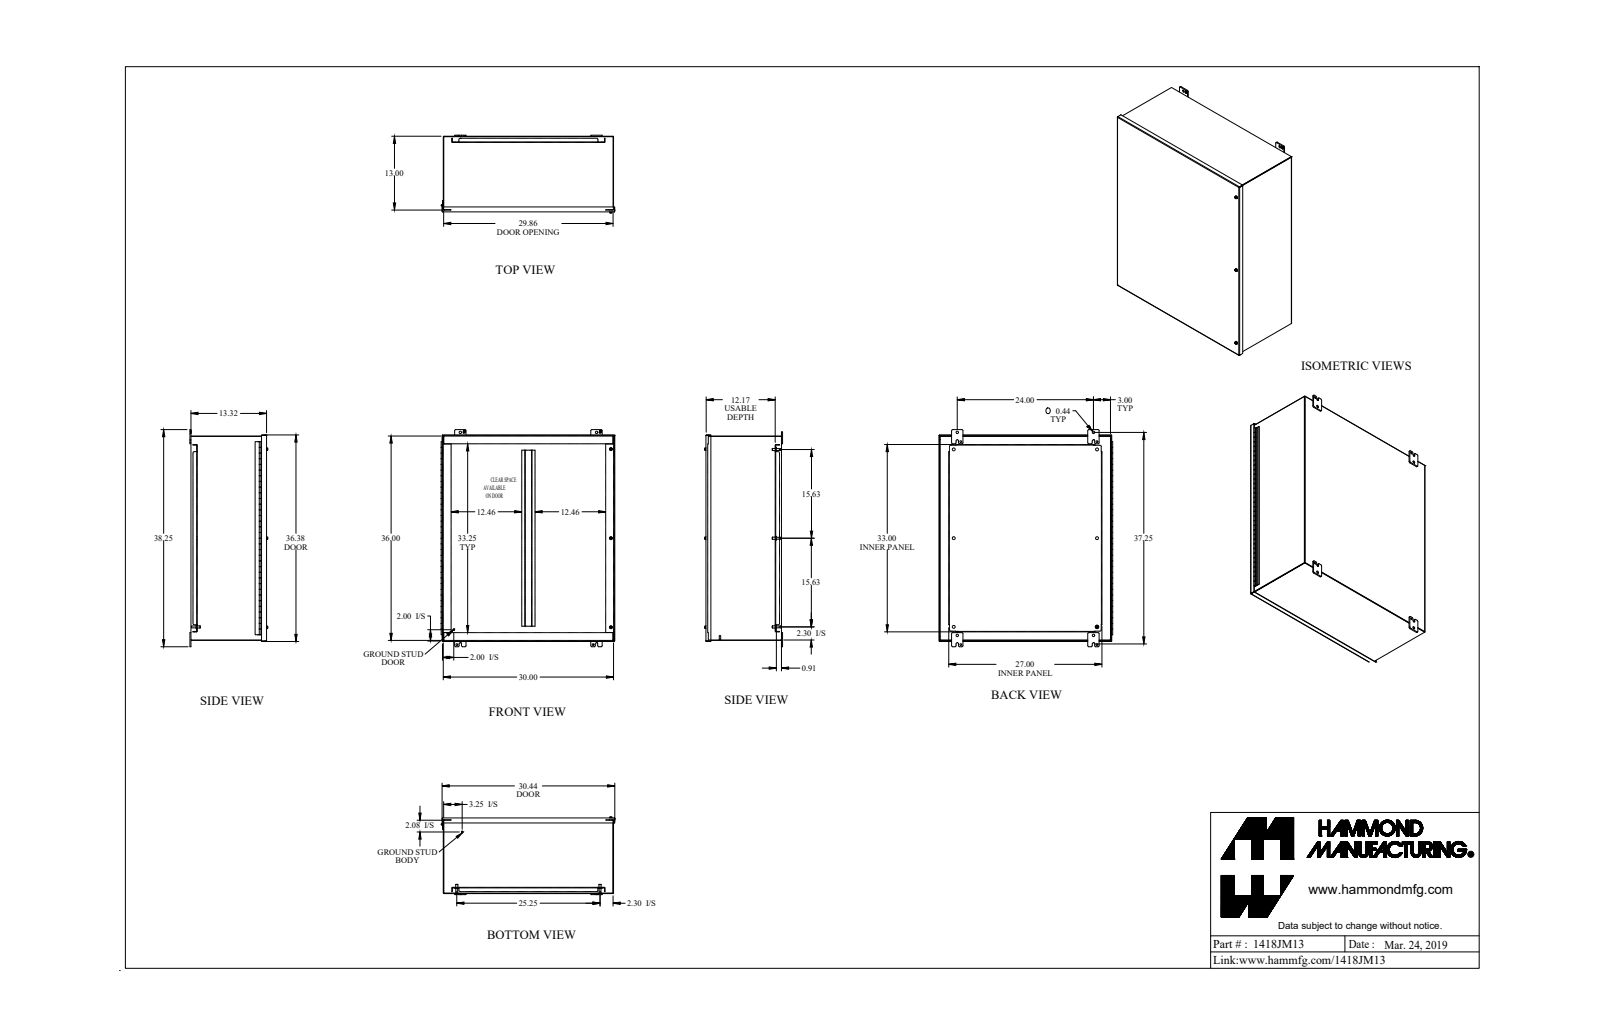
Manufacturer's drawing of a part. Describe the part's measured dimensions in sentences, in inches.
The part is named "1418JM13_Default". Its 3-D file was written by "SolidWorks 2018 (CONFIG_CONTROL_DESIGN)". It is 48 solids with 1273 faces: 752 planar, 459 cylindrical and 62 other. Overall it measures 38.25 by 30.604 by 13.721 inches. Its volume is 455.6 cubic inches and its surface area 11 551 square inches. Round holes: 7 of diameter 0.313, 6 of diameter 0.5, 4 of diameter 0.307, 4 of diameter 0.437, 4 of diameter 0.445, 3 of diameter 0.26, 3 of diameter 0.266, 3 of diameter 0.28, 3 of diameter 0.29, 3 of diameter 0.397, 1 of diameter 0.187, 1 of diameter 3.5. Round bosses or shafts: 6 of diameter 0.65, 6 of diameter 0.375, 6 of diameter 0.33, 4 of diameter 1, 3 of diameter 0.51, 3 of diameter 0.5, 3 of diameter 0.39, 3 of diameter 0.244. Partial cylindrical surfaces (rounded edges, fillets, slot ends): 35 of radius 0.188, 28 of radius 0.25, 16 of radius 0.116, 10 of radius 0.036, 10 of radius 0.108, 8 of radius 0.218, 7 of radius 0.125, 6 of radius 0.133. The main face-to-face distances are 0.072, 13.25, 13.178, 13.322, 0.095, 29.928, 12.146, 1.104, 1.032, 12.218. The hole center spacings are 27.156, 31.25, 1.735, 24, 35.75, 43.059, 3.065, 15.625.
